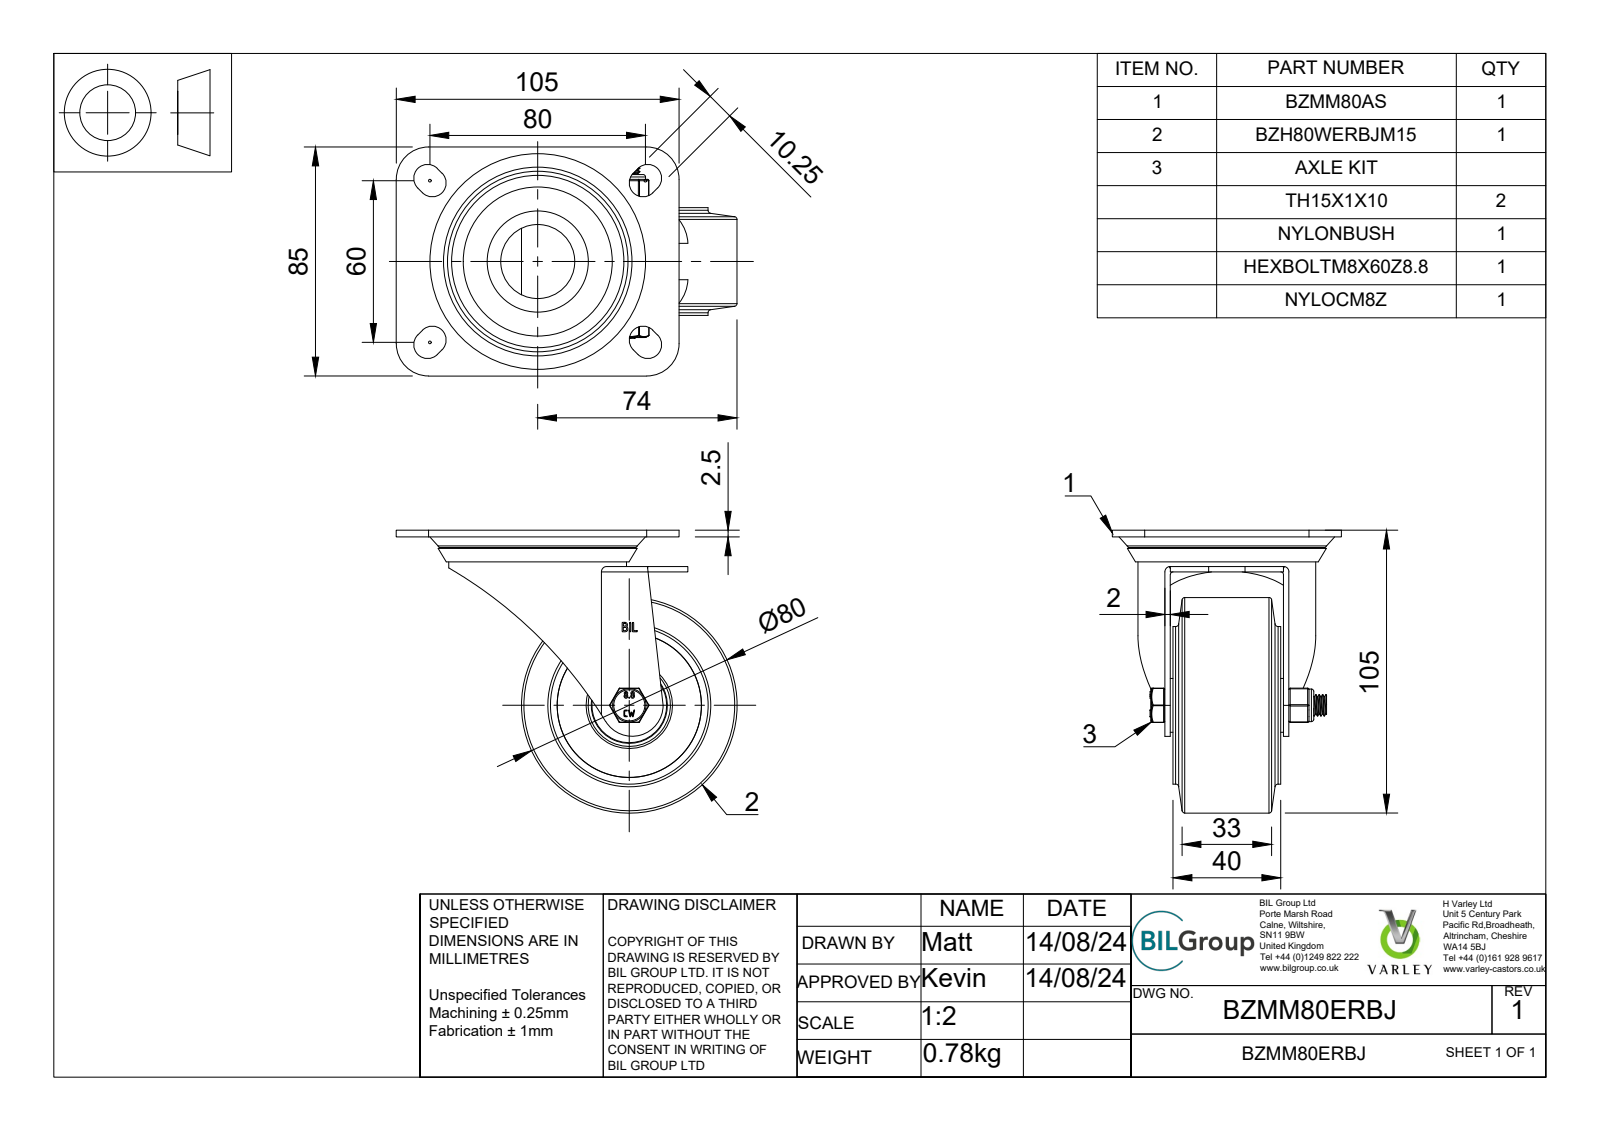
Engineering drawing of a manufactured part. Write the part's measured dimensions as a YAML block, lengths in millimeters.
part_name: "BZMM80ERBJ v3; BZMM80AS - 2 - 42 v1; ZINC PLATED, PRESSED STEEL TOP PLATE 1; ZINC PLATED, PRESSED STEEL TOP PLATE 1 Geometry (+7 more)"
step_written_by: "Autodesk Translation Framework v13.14.0.145 (AUTOMOTIVE_DESIGN)"
units: millimeters
bodies: {solids: 64, faces: 1150, planar: 378, cylindrical: 218, other: 554}
overall_size: [126.5, 105, 85]
volume: 228838
surface_area: 107298
round_holes:
  - {diameter: 0.66, count: 2}
  - {diameter: 8, count: 1}
  - {diameter: 8.2, count: 1}
  - {diameter: 8.6, count: 1}
  - {diameter: 10.25, count: 1}
  - {diameter: 15, count: 1}
  - {diameter: 20.5, count: 1}
  - {diameter: 26.8, count: 1}
  - {diameter: 27.5, count: 1}
  - {diameter: 28, count: 1}
  - {diameter: 28.2, count: 1}
  - {diameter: 32, count: 1}
round_bosses_or_shafts:
  - {diameter: 80, count: 1}
  - {diameter: 66, count: 1}
  - {diameter: 58.5, count: 1}
  - {diameter: 31.5, count: 1}
  - {diameter: 21.5, count: 1}
  - {diameter: 20, count: 1}
  - {diameter: 19, count: 1}
  - {diameter: 14.75, count: 1}
partial_cylinders:
  - {radius: 0.5, count: 18}
  - {radius: 0.25, count: 12}
  - {radius: 5.12, count: 8}
  - {radius: 0.33, count: 4}
  - {radius: 0.64, count: 4}
  - {radius: 1, count: 4}
  - {radius: 12, count: 4}
  - {radius: 0.63, count: 2}
face_to_face_distances: [2.5, 2, 3, 0.5, 41, 1, 44, 43, 10.5, 40]
hole_center_spacings: [4.65, 2.49]
